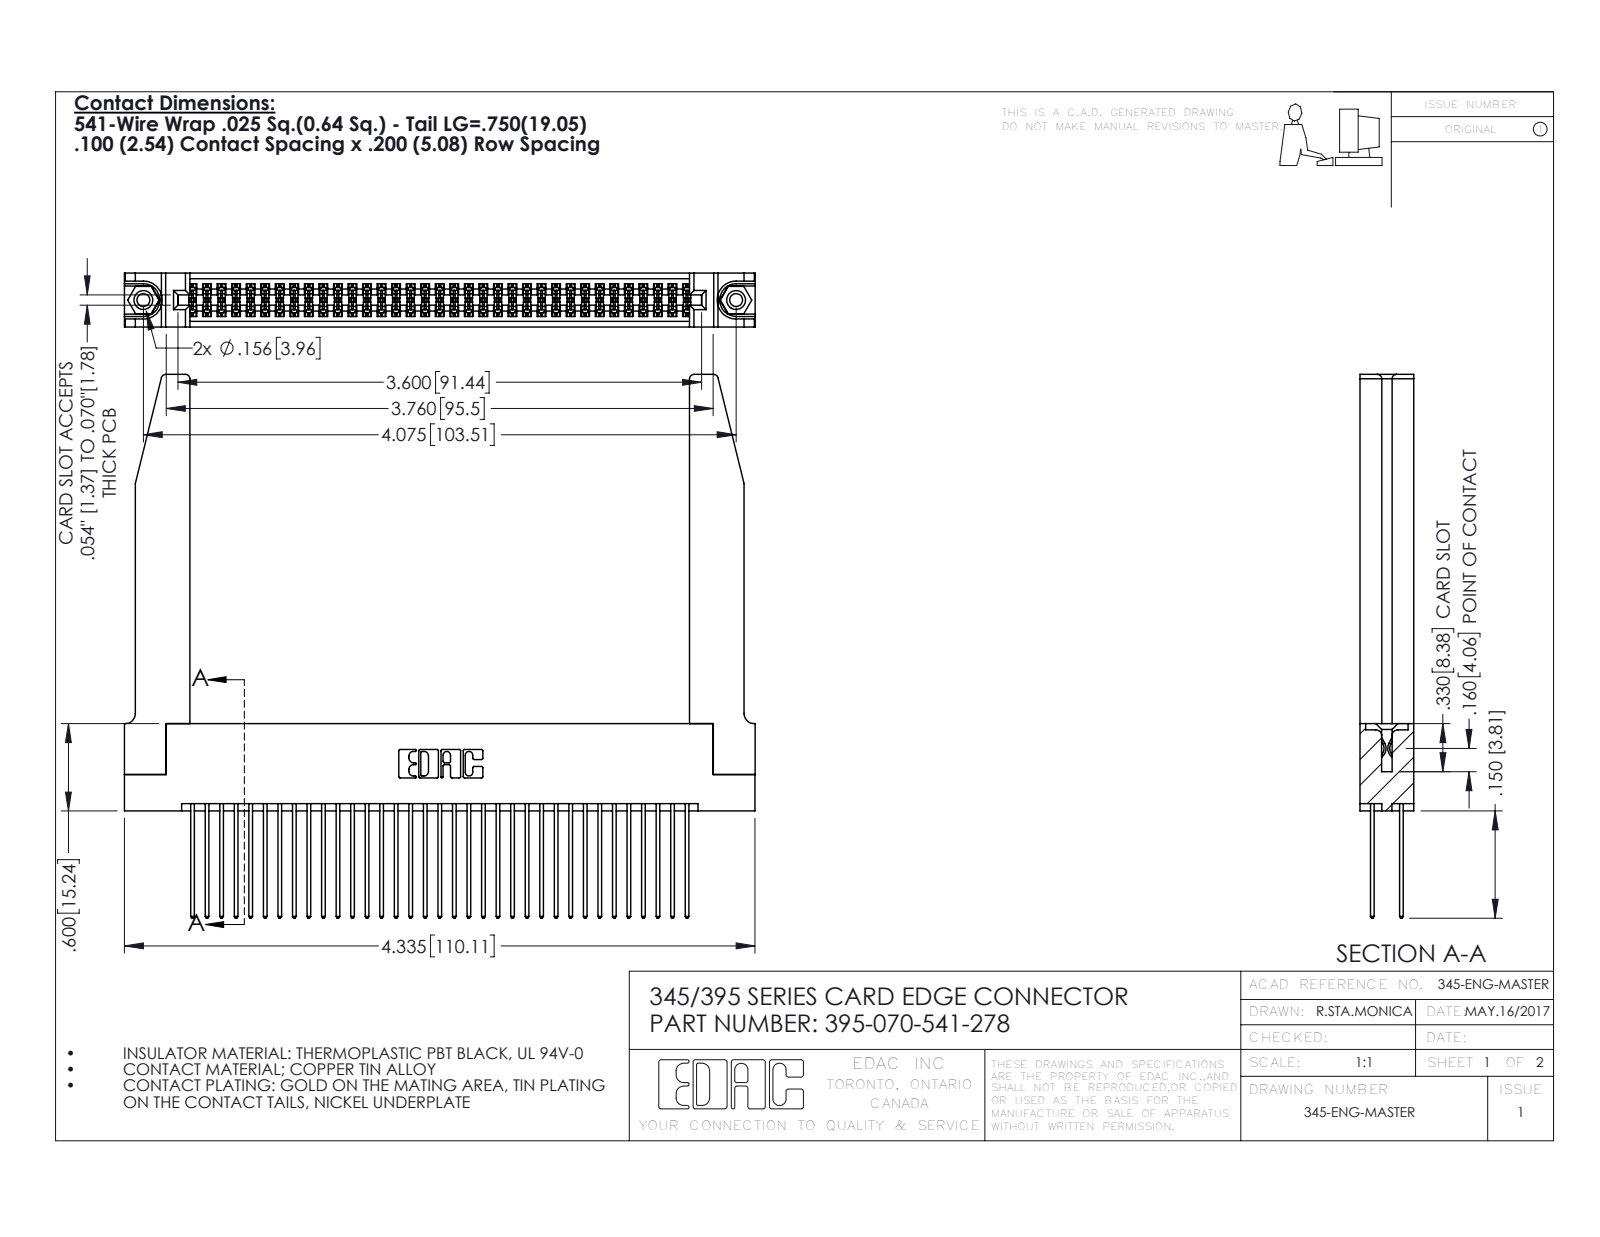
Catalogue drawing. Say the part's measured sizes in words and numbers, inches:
The part is named "345 Part_Flush Mounting Lugs - 0.156 Dia-TH; 345-220-078_345-220-078; 345-292-001_345-293-141; 345-250-001_345-250-001-102 (+1 more)". Its 3-D file was written by "SolidWorks 2016 (CONFIG_CONTROL_DESIGN)". It is 75 solids with 3860 faces: 2532 planar, 1276 cylindrical and 52 other. Overall it measures 4.336 by 3.737 by 0.37 inches. Its volume is 1.148 cubic inches and its surface area 38.6 square inches. Round holes: 2 of diameter 0.089, 2 of diameter 0.125, 2 of diameter 0.156, 1 of diameter 0.064. Round bosses or shafts: 2 of diameter 0.155. Partial cylindrical surfaces (rounded edges, fillets, slot ends): 105 of radius 0.006, 70 of radius 0.01, 22 of radius 0.01, 8 of radius 0.03, 6 of radius 0.007, 6 of radius 0.031, 3 of radius 0.026, 2 of radius 0.014. The main face-to-face distances are 0.072, 0.298, 0.37, 0.2, 0.098, 0.272, 0.025, 0.225, 0.175, 0.148. The hole center spacings are 0.27, 3.839, 4.075.
